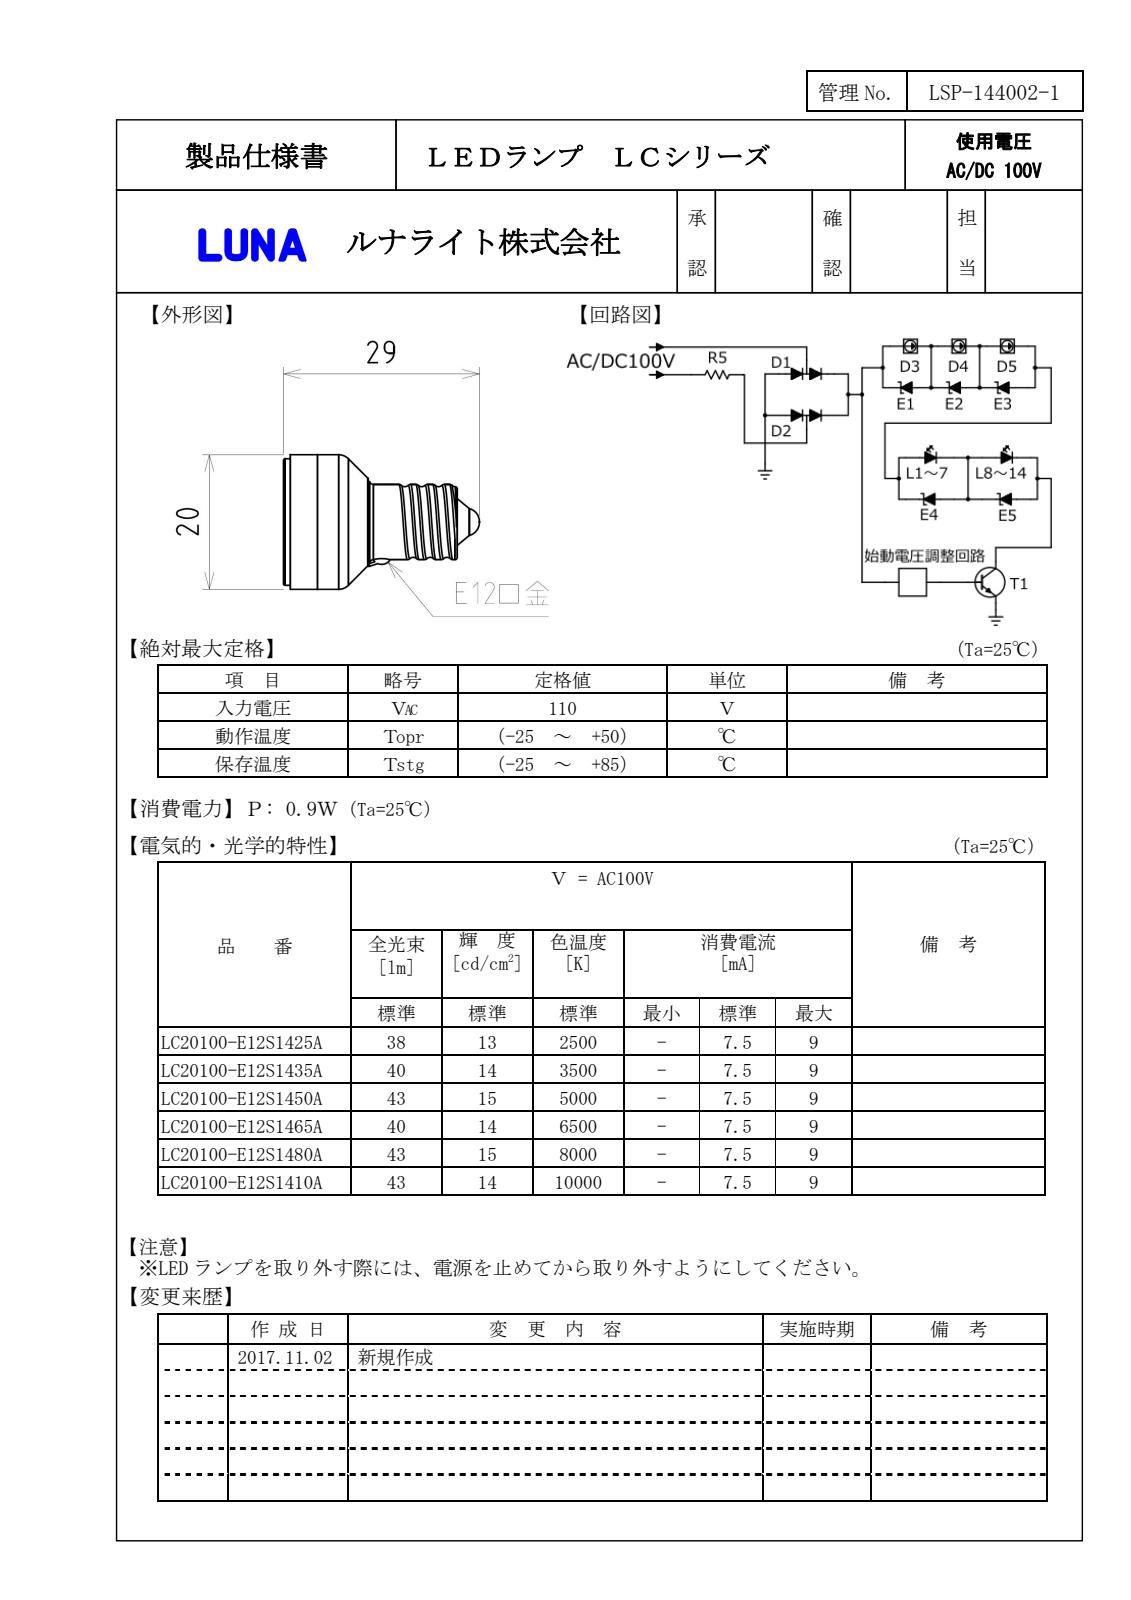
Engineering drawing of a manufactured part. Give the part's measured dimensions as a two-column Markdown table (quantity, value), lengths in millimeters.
| quantity | value |
| --- | --- |
| part name | 0-160044HP |
| STEP written by | SolidWorks 2019 (AUTOMOTIVE_DESIGN) |
| units | millimeters |
| bodies | 26 solids, 570 faces (385 planar, 134 cylindrical, 51 other) |
| overall size | 40 × 20 × 20 |
| volume | 5 703 mm³ |
| surface area | 5 047 mm² |
| round holes (diameter × count) | 0.5 × 2, 16.2 × 1 |
| round bosses / shafts (diameter × count) | 0.4 × 5, 20 × 1, 18.8 × 1, 17.4 × 1, 12 × 1, 11.2 × 1, 9.9 × 1 |
| partial cylindrical surfaces (radius × count) | 0.2 × 56, 0.25 × 6, 0.46 × 4, 8 × 1, 8.8 × 1, 9.5 × 1 |
| main face-to-face distances | 1.4, 1, 2, 2.4, 4.4, 3.4, 8.9, 5.5, 7.5, 9.9 |
| hole center spacings | 6.6, 3.2 |
